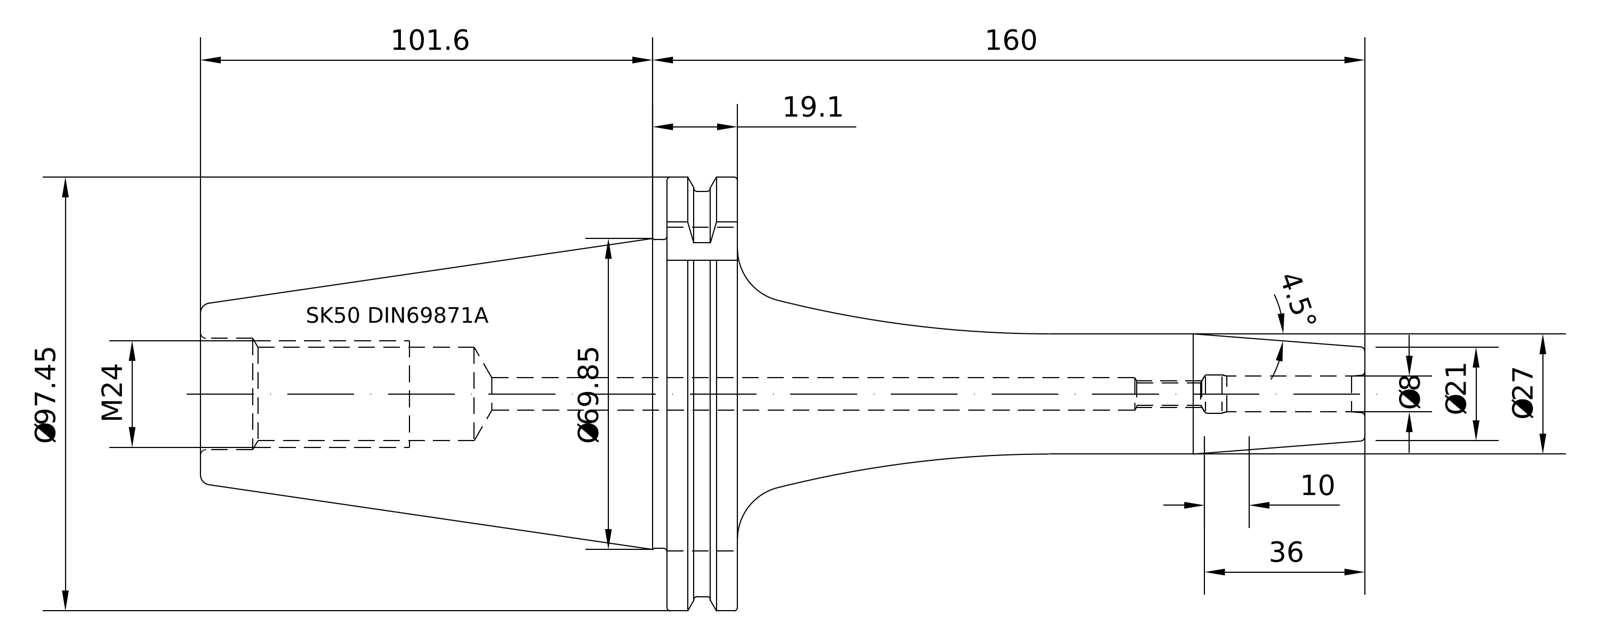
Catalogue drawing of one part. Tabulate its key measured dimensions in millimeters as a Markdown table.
| quantity | value |
| --- | --- |
| part name | 50-442-08 |
| STEP written by | PRO/ENGINEER BY PARAMETRIC TECHNOLOGY CORPORATION, 2010430 (CONFIG_CONTROL_DESIGN) |
| units | millimeters |
| bodies | 1 solid, 95 faces (21 planar, 24 cylindrical, 50 other) |
| overall size | 261.6 × 97.47 × 94 |
| volume | 440 265 mm³ |
| surface area | 54 956 mm² |
| round holes (diameter × count) | 8 × 1, 20.75 × 1, 25.01 × 1, 25.7 × 1 |
| round bosses / shafts (diameter × count) | 91 × 1, 69.15 × 1, 27 × 1, 24.01 × 1 |
| partial cylindrical surfaces (radius × count) | 1.75 × 1, 48.74 × 1 |
| main face-to-face distances | 15.85, 72.8, 104.8, 120.65, 25.8, 261.6, 156.8, 140.95, 48, 56.8 |
